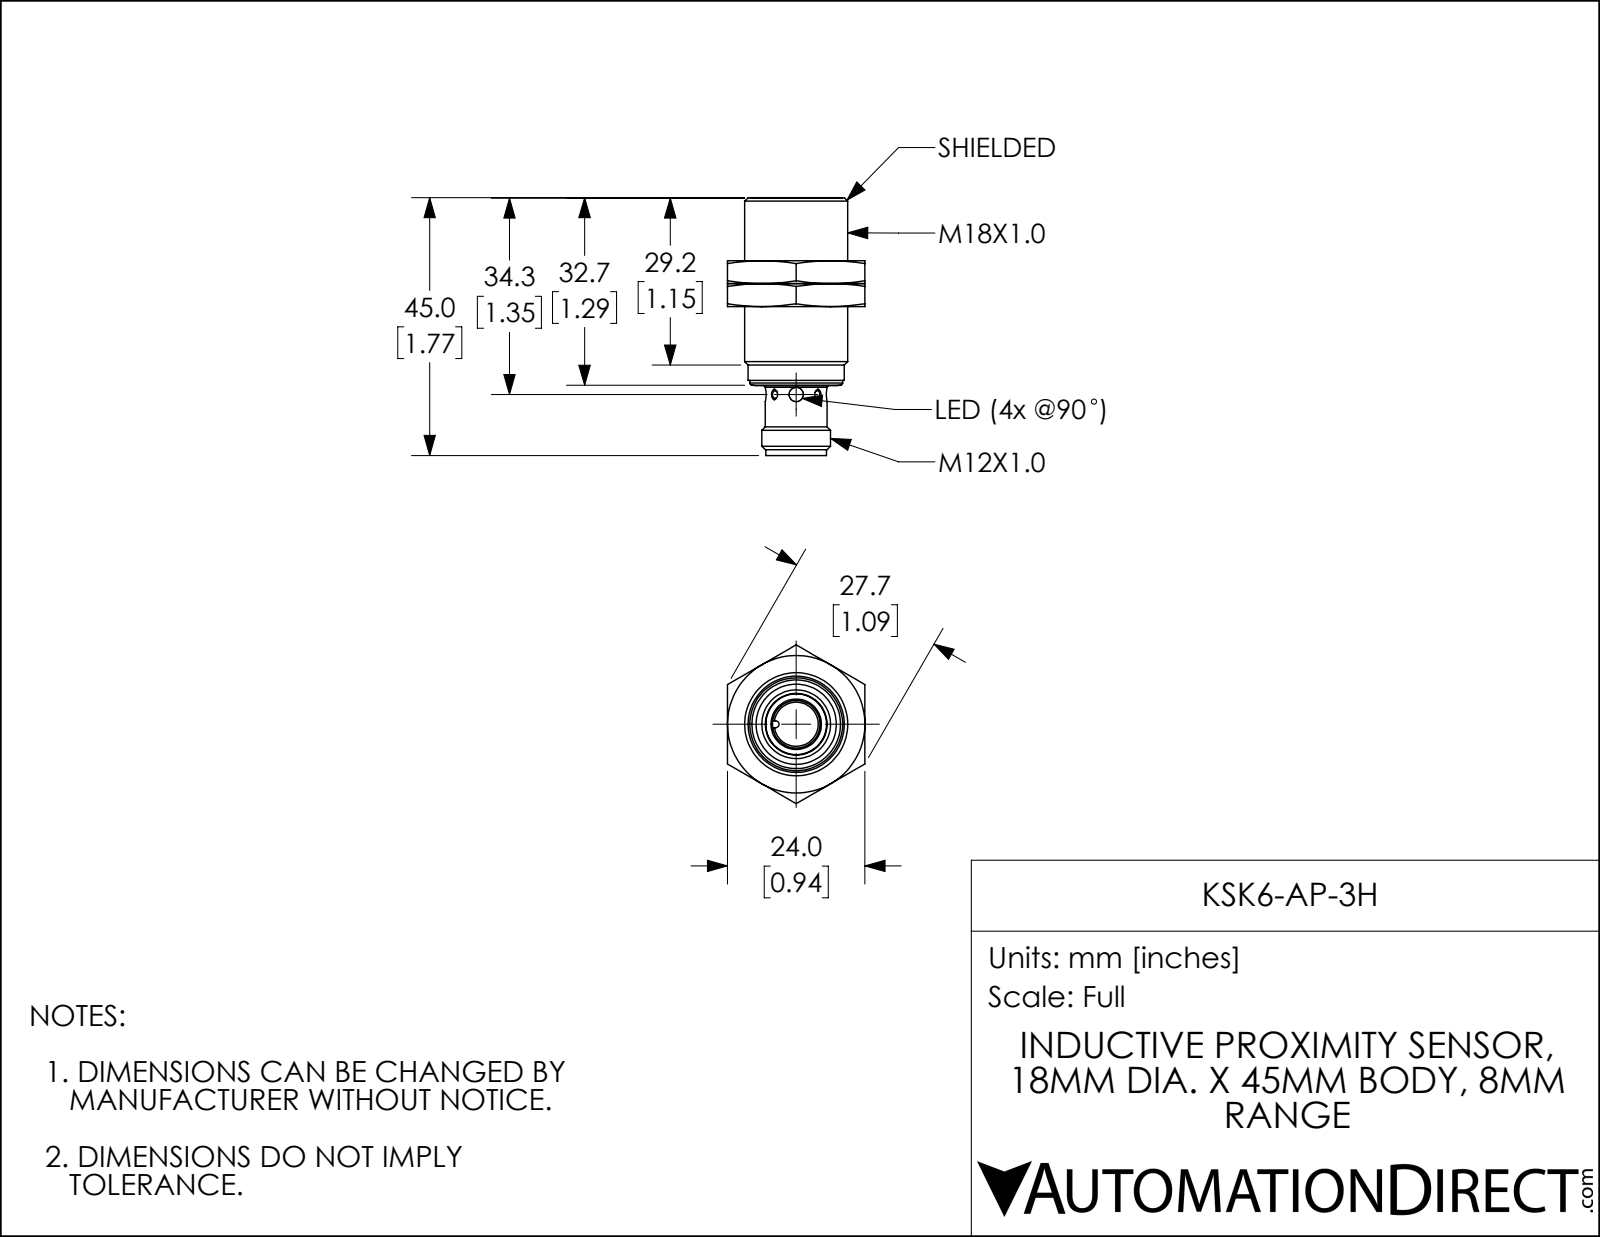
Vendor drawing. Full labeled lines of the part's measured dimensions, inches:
Part name (STEP PRODUCT): KSK6-AP-3H
STEP written by: SolidWorks 2017 (AUTOMOTIVE_DESIGN)
Units: inches
Bodies: 3 solids, 95 faces (28 planar, 17 cylindrical, 50 other)
Overall size (bounding box): 1.772 × 1.091 × 0.945
Volume: 0.672 in³ · Surface area: 7.975 in²
Round holes (diameter × count): ⌀0.327 ×1, ⌀0.61 ×1, ⌀0.634 ×1, ⌀0.666 ×1
Round bosses / shafts (diameter × count): ⌀0.709 ×1, ⌀0.661 ×1, ⌀0.638 ×1, ⌀0.632 ×1, ⌀0.472 ×1, ⌀0.425 ×1, ⌀0.417 ×1
Partial cylindrical surfaces — rounded edges, fillets, slot ends (radius × count): R0.213 ×4, R0.024 ×1
Main face-to-face distances: 0.157, 0.945, 0.315, 0.746, 0.589, 0.431, 0.543, 0.701, 0.858, 1.289
